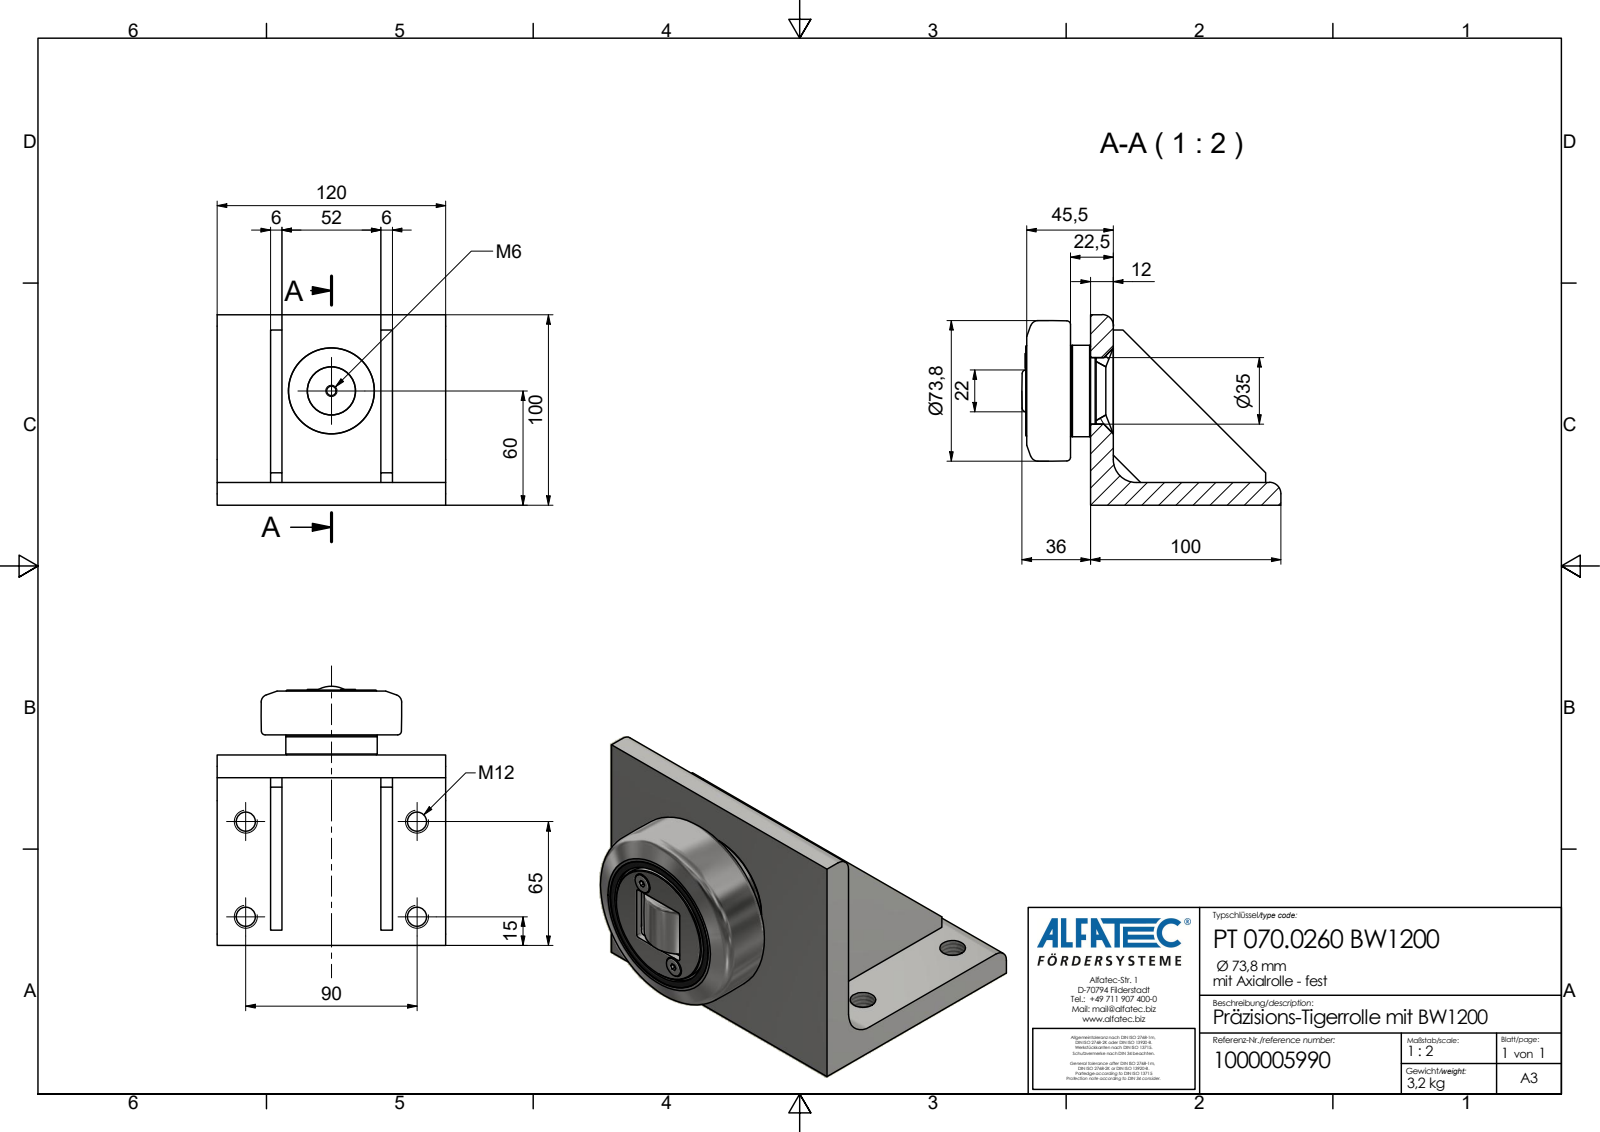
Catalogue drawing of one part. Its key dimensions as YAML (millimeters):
part_name: "PT 070.0260 BW1200_Kontur"
step_written_by: "Autodesk Inventor 2020 (AP242_MANAGED_MODEL_BASED_3D_ENGINEERING_MIM_LF)"
units: millimeters
bodies: {solids: 1, faces: 81, planar: 50, cylindrical: 18, other: 13}
overall_size: [136, 120, 100]
volume: 421431
surface_area: 77824
round_holes:
  - {diameter: 10.11, count: 4}
  - {diameter: 2.5, count: 1}
  - {diameter: 4.92, count: 1}
round_bosses_or_shafts:
  - {diameter: 7.8, count: 2}
  - {diameter: 48, count: 1}
  - {diameter: 47.3, count: 1}
partial_cylinders:
  - {radius: 1, count: 4}
  - {radius: 6, count: 2}
  - {radius: 12, count: 1}
face_to_face_distances: [12, 6, 58, 34, 92, 28, 86, 64, 52, 120]
hole_center_spacings: [50, 90, 102.96]
